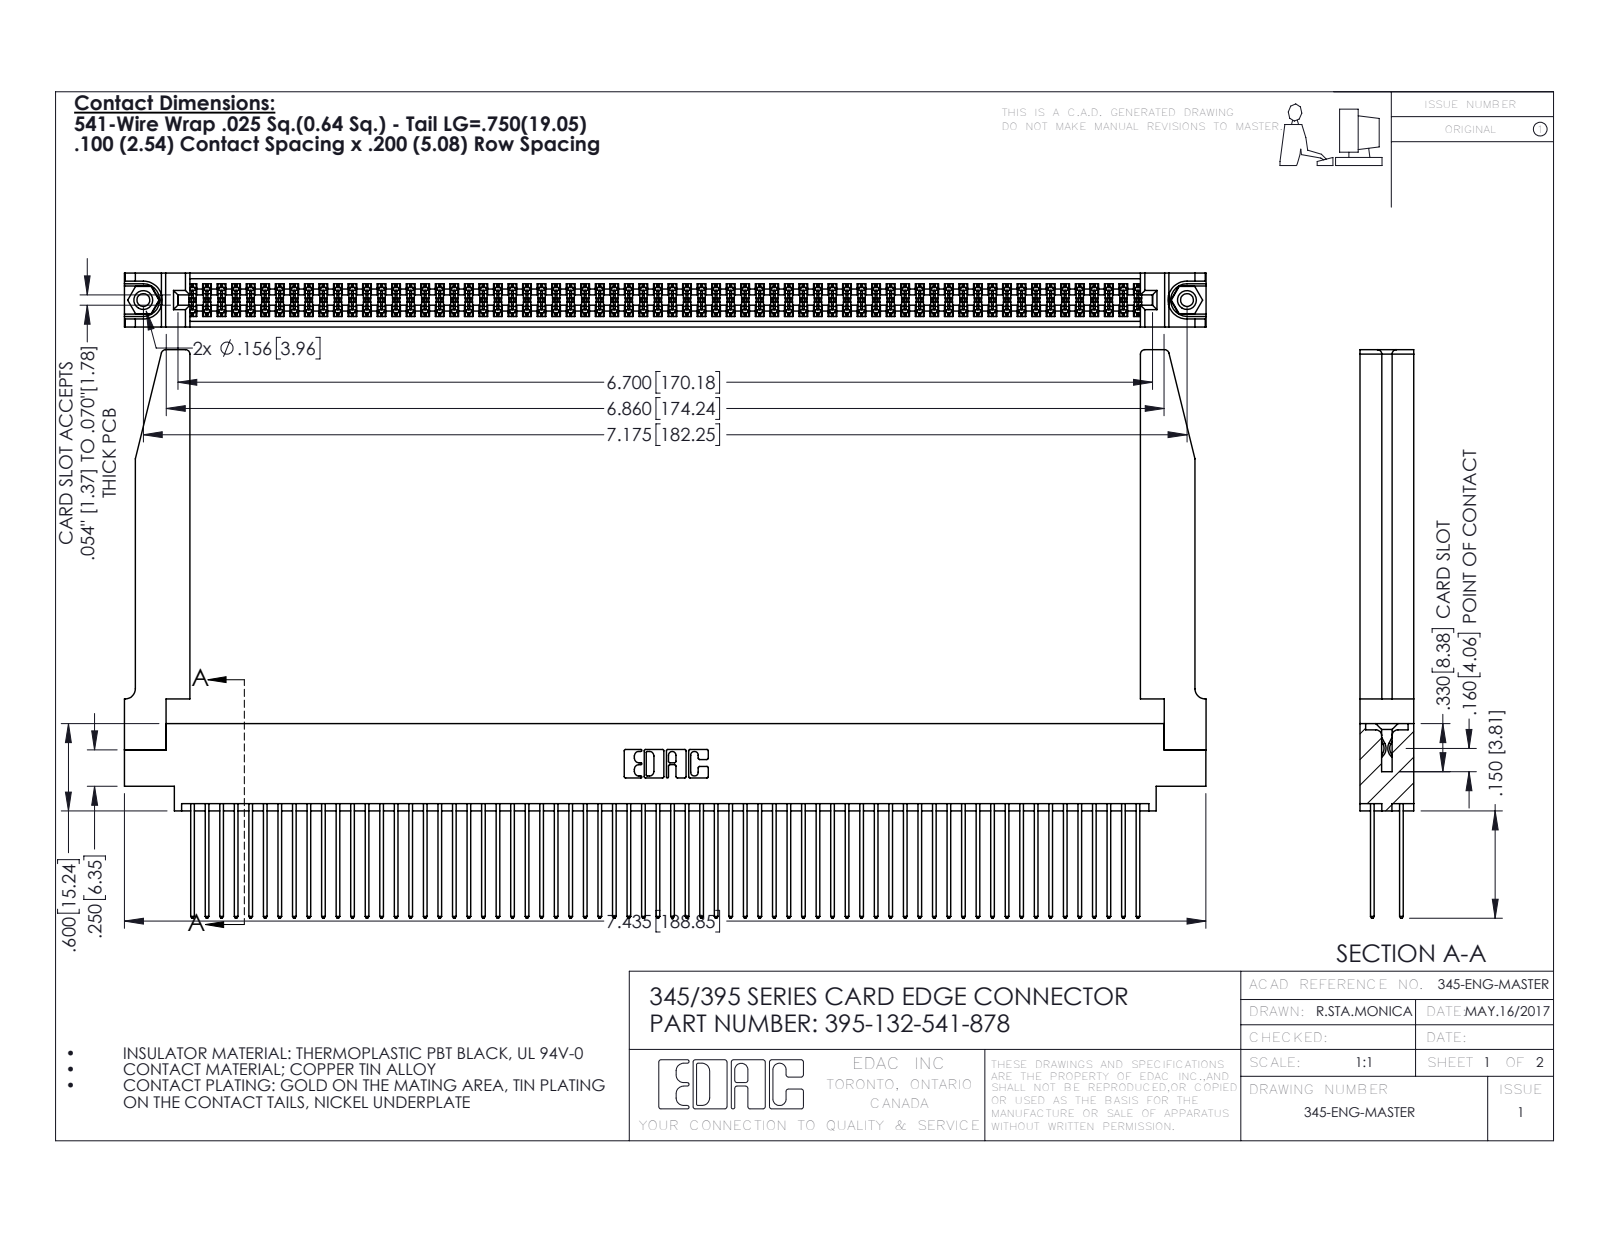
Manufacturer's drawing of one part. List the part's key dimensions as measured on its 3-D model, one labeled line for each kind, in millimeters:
Part name (STEP PRODUCT): 345-220-078_345-220-078; 345 Part_0.170 Offset - 0.156 Dia-TH; 345-292-001_345-293-141; 395-132-541-878 (+1 more)
STEP written by: SolidWorks 2016 (CONFIG_CONTROL_DESIGN)
Units: millimetres
Bodies: 137 solids, 6964 faces (4582 planar, 2330 cylindrical, 52 other)
Overall size (bounding box): 188.9 × 99.2 × 9.4
Volume: 26 990 mm³ · Surface area: 39 410 mm²
Round holes (diameter × count): ⌀2.3 ×2, ⌀3.2 ×2, ⌀4 ×2, ⌀1.6 ×1
Round bosses / shafts (diameter × count): ⌀3.9 ×2
Partial cylindrical surfaces — rounded edges, fillets, slot ends (radius × count): R0.2 ×198, R0.3 ×132, R0.3 ×22, R0.8 ×8, R0.2 ×6, R0.8 ×6, R0.7 ×3, R0.4 ×2
Main face-to-face distances: 1.8, 7.6, 9.4, 2.5, 6.9, 0.6, 5.1, 5.7, 4.4, 3.8
Hole centre spacings: 6.9, 176.3, 182.2
